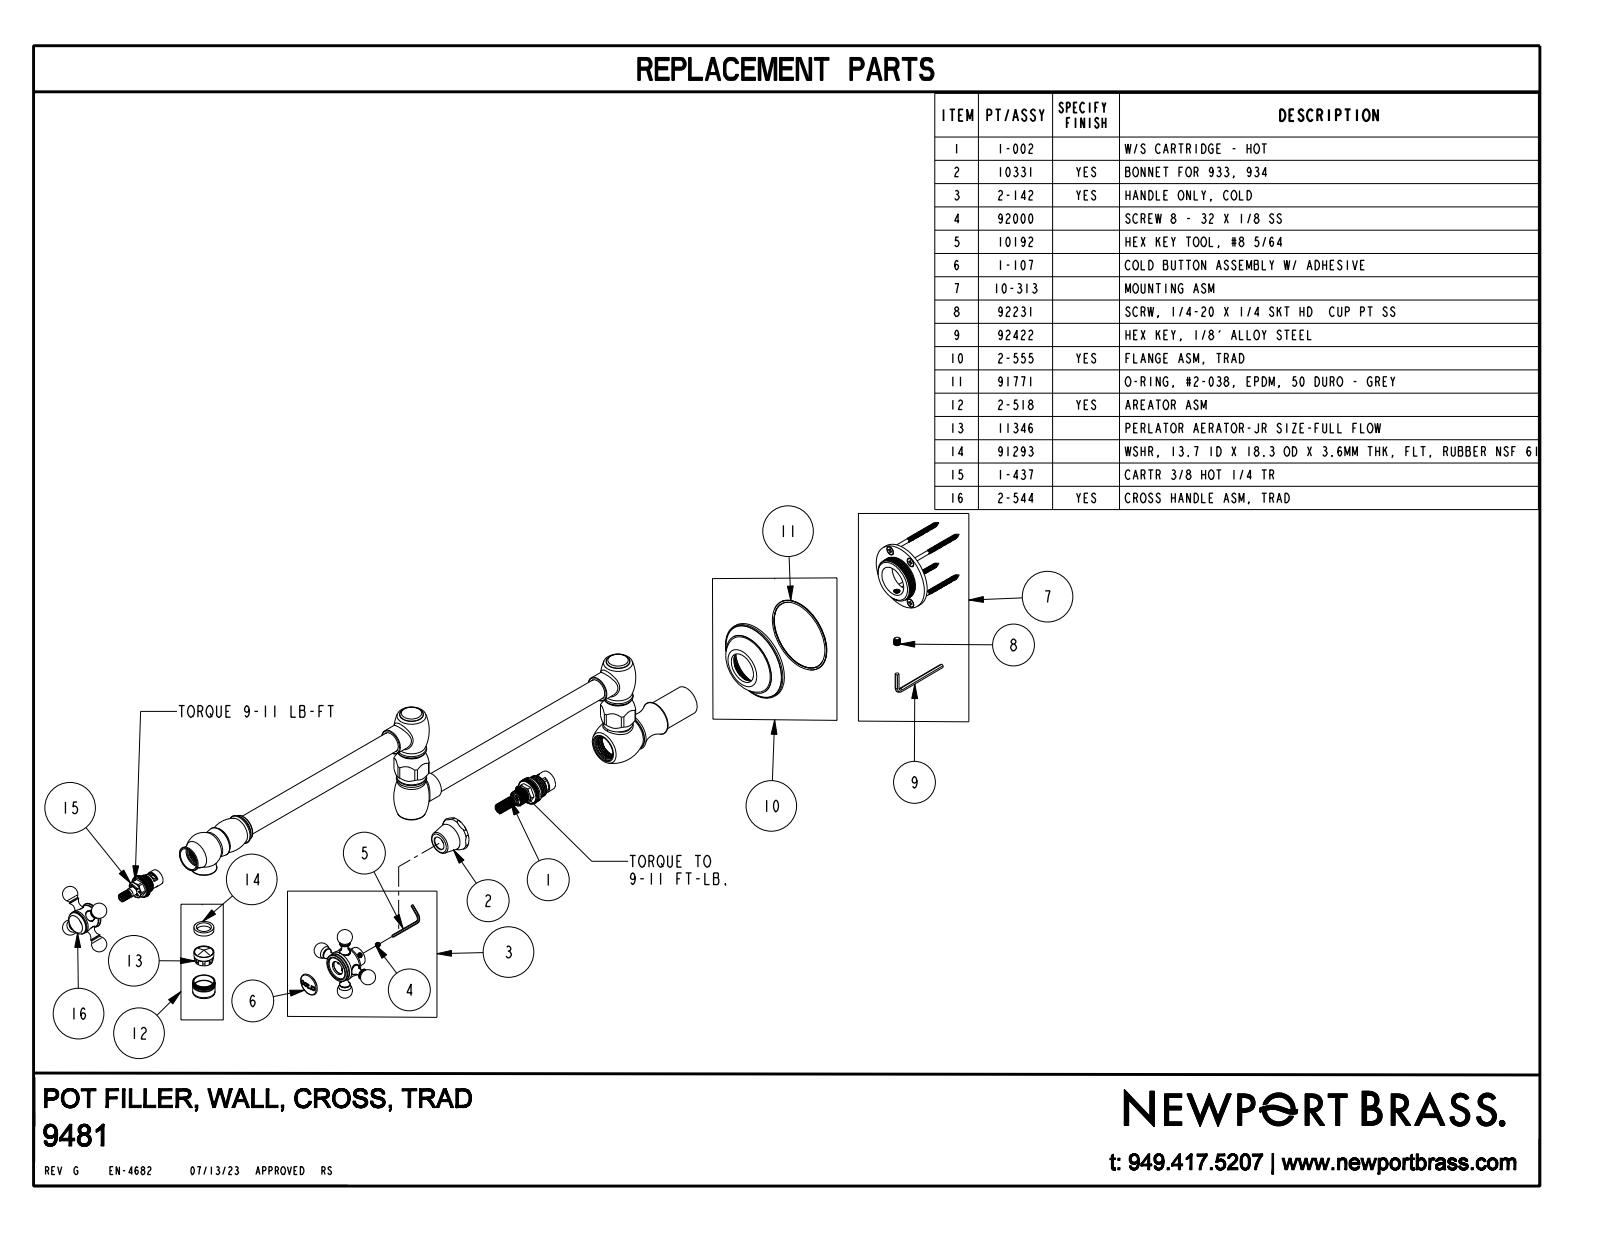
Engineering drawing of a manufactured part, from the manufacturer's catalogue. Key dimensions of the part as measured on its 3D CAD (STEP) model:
Part name (STEP PRODUCT): 9481
STEP written by: CREO PARAMETRIC BY PTC INC, 2018400 (CONFIG_CONTROL_DESIGN)
Units: inches
Bodies: 1 solid, 475 faces (94 planar, 114 cylindrical, 267 other)
Overall size (bounding box): 26.37 × 8.188 × 2.92
Volume: 29.16 in³ · Surface area: 136.9 in²
Round holes (diameter × count): ⌀0.41 ×3, ⌀0.4 ×1, ⌀0.794 ×1
Round bosses / shafts (diameter × count): ⌀0.94 ×4, ⌀0.392 ×4, ⌀0.75 ×2, ⌀2.92 ×1, ⌀2.29 ×1, ⌀1.082 ×1, ⌀1.055 ×1, ⌀1 ×1
Partial cylindrical surfaces — rounded edges, fillets, slot ends (radius × count): R0.03 ×5, R0.006 ×3, R0.048 ×3, R0.018 ×2, R0.65 ×2, R0.054 ×1, R0.062 ×1, R0.07 ×1
Main face-to-face distances: 1.17, 0.02, 0.69, 1.17, 9.152, 10.322, 7.982, 9.152, 20.285, 0.233
Hole centre spacings: 8.156
